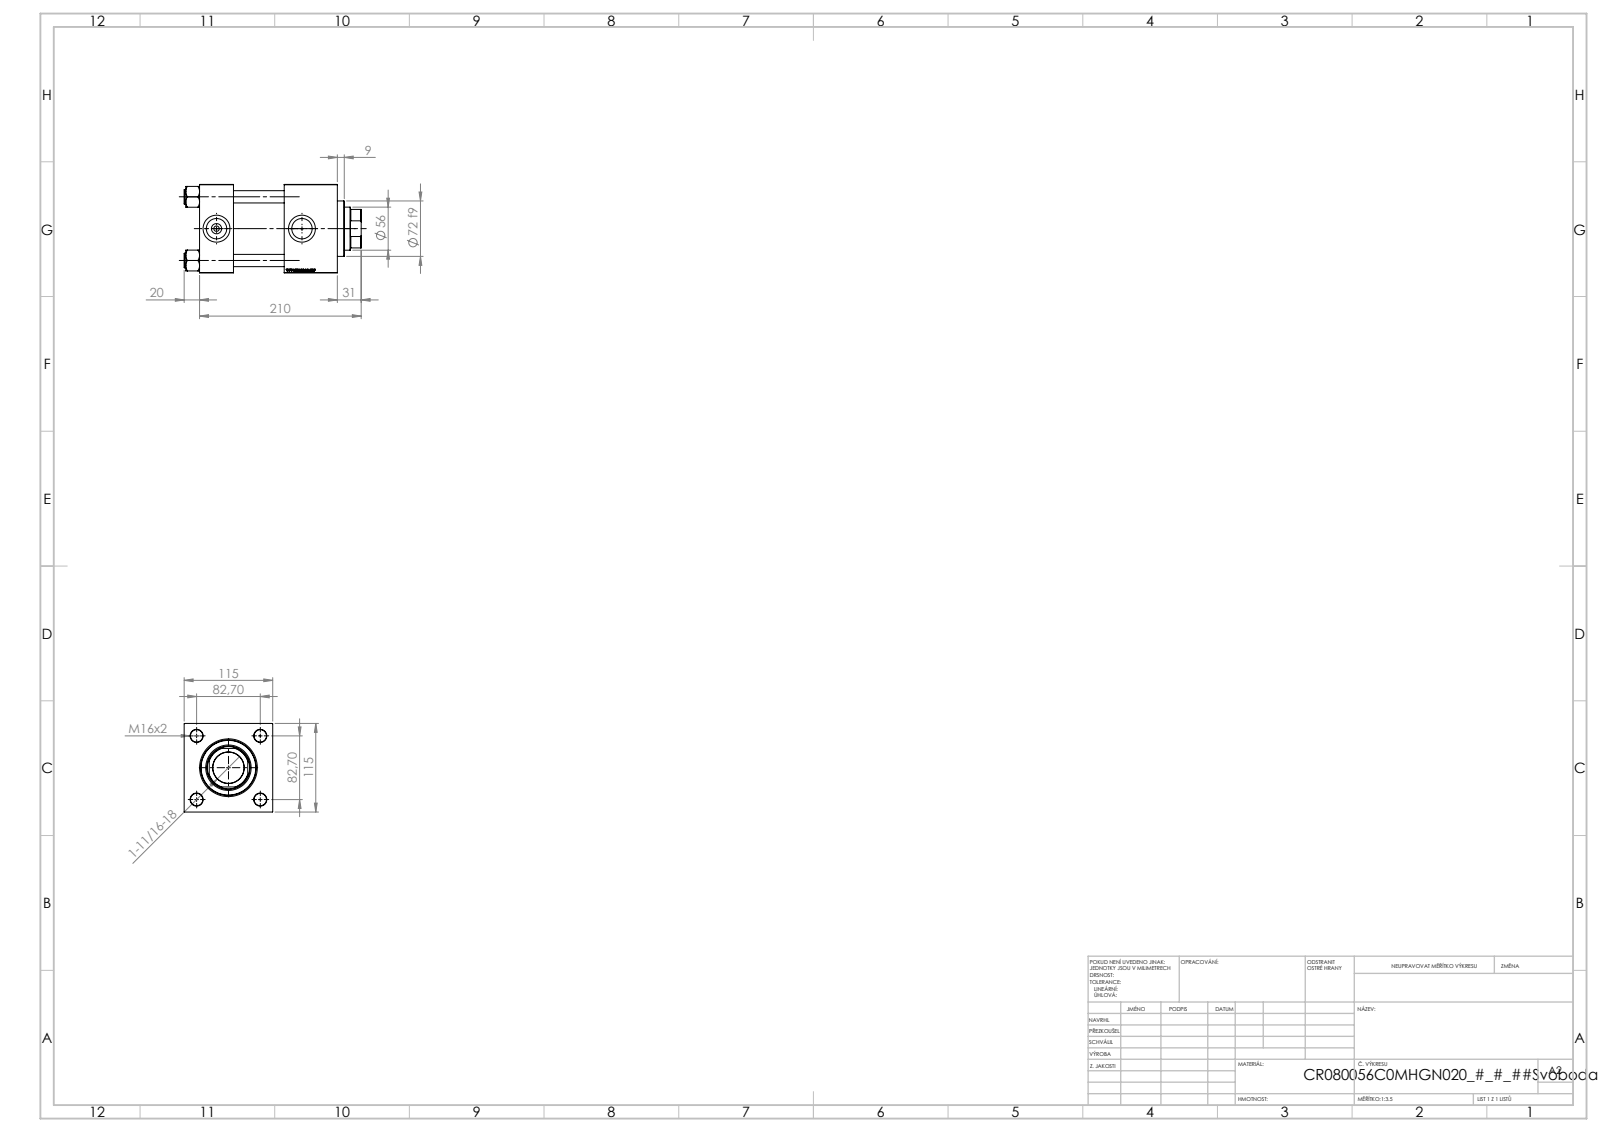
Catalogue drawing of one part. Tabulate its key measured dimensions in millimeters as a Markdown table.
| quantity | value |
| --- | --- |
| part name | V215CR_VCP_C; V215CR_C_TYCINKA; V215_VC_A; V215CR_C_Body (+1 more) |
| STEP written by | SolidWorks 2019 (CONFIG_CONTROL_DESIGN) |
| units | millimeters |
| bodies | 11 solids, 1193 faces (573 planar, 84 cylindrical, 536 other) |
| overall size | 230 × 115 × 115 |
| volume | 1 862 000 mm³ |
| surface area | 280 215 mm² |
| round holes (diameter × count) | 16 × 4, 7 × 2, 26.44 × 2, 35 × 2, 40.5 × 1, 56 × 1, 59 × 1, 61 × 1, 72 × 1, 80 × 1 |
| round bosses / shafts (diameter × count) | 19 × 4, 86 × 1 |
| partial cylindrical surfaces (radius × count) | 27 × 1 |
| main face-to-face distances | 115, 44, 110, 66, 179, 135, 69, 20, 150.3, 106.3 |
| hole center spacings | 58.48, 82.7, 116.96, 111 |
